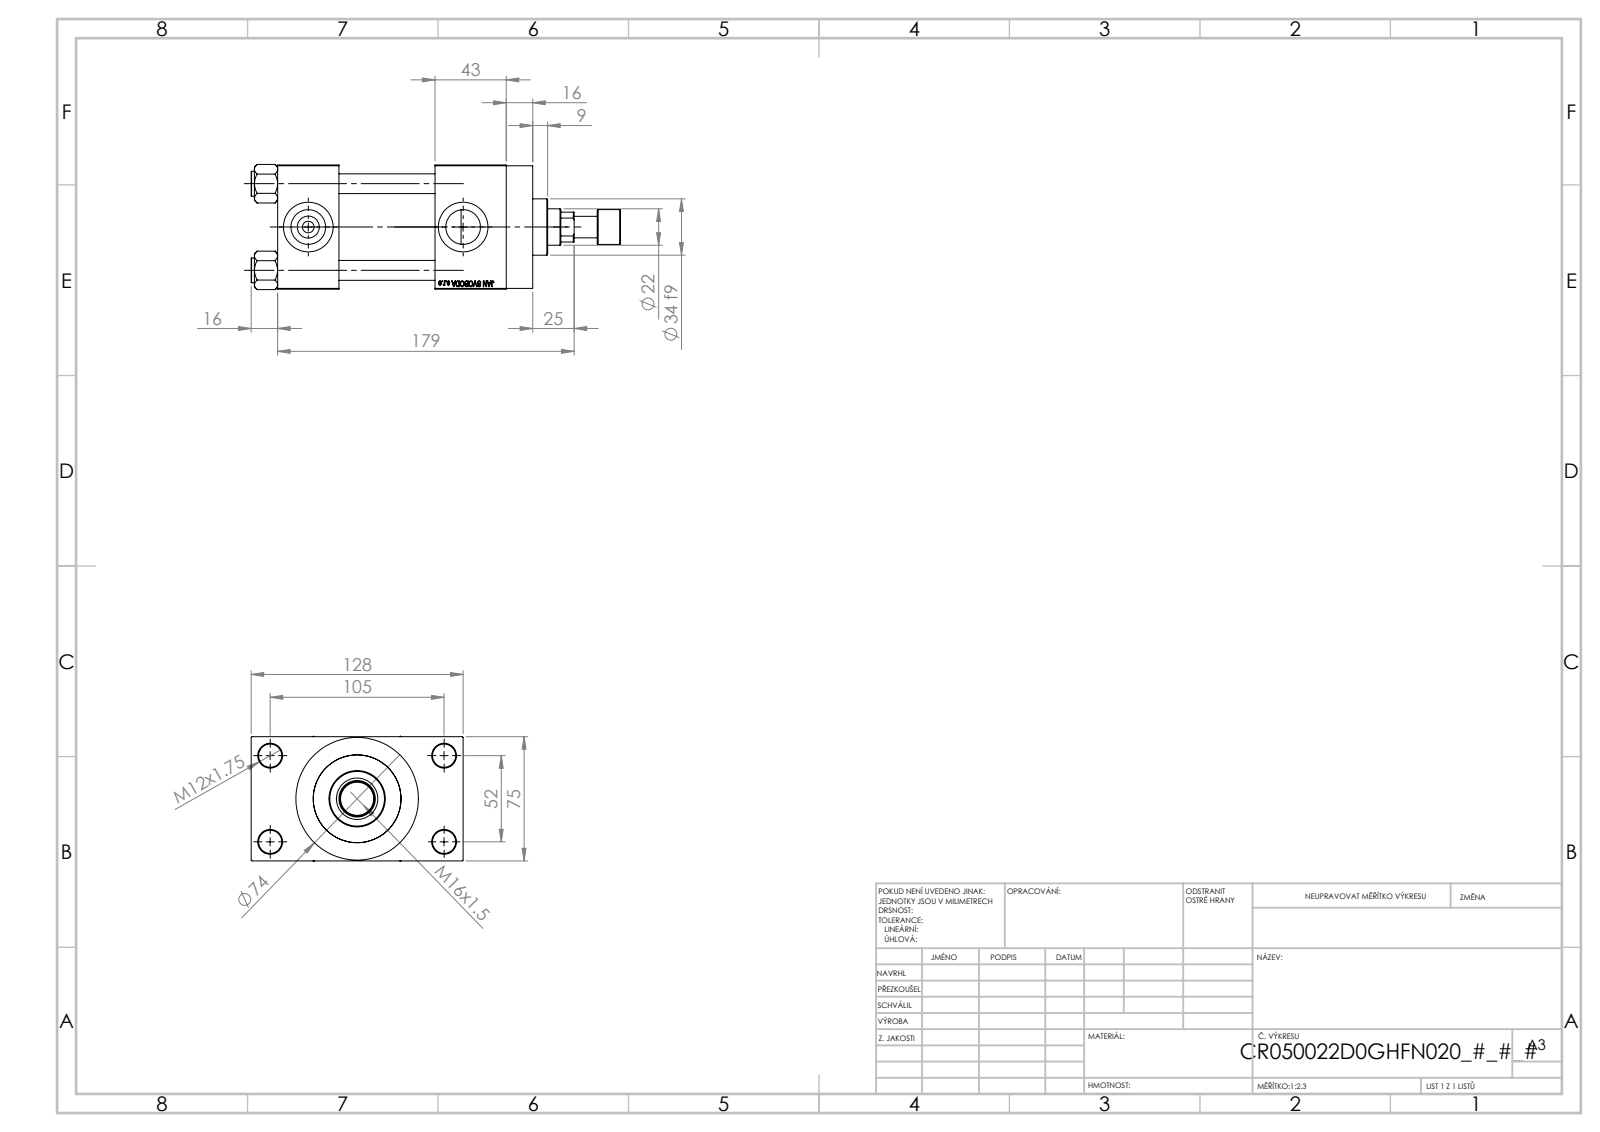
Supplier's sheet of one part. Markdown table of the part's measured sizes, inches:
| quantity | value |
| --- | --- |
| part name | V215CR_VCP_D; V215CR_D_TYCINKA; NUT_M5_D; V215CR_ROD_END_F (+2 more) |
| STEP written by | SolidWorks 2019 (CONFIG_CONTROL_DESIGN) |
| units | inches |
| bodies | 12 solids, 1114 faces (500 planar, 92 cylindrical, 522 other) |
| overall size | 8.78 × 5.039 × 2.974 |
| volume | 49.08 in³ |
| surface area | 261.7 in² |
| round holes (diameter × count) | 0.472 × 4, 0.551 × 4, 0.276 × 2, 0.825 × 2, 1.181 × 2, 0.413 × 1, 0.866 × 1, 0.984 × 1, 1.614 × 1, 1.969 × 1, 2.087 × 1 |
| round bosses / shafts (diameter × count) | 0.591 × 4, 2.913 × 1, 2.205 × 1, 1.339 × 1, 0.827 × 1, 0.512 × 1 |
| main face-to-face distances | 2.953, 2.283, 1.457, 3.74, 1.043, 5.433, 3.976, 1.693, 3.996, 0.63 |
| hole center spacings | 1.037, 1.456, 2.059, 2.3, 2.307, 3.096, 3.715, 2.047 |
